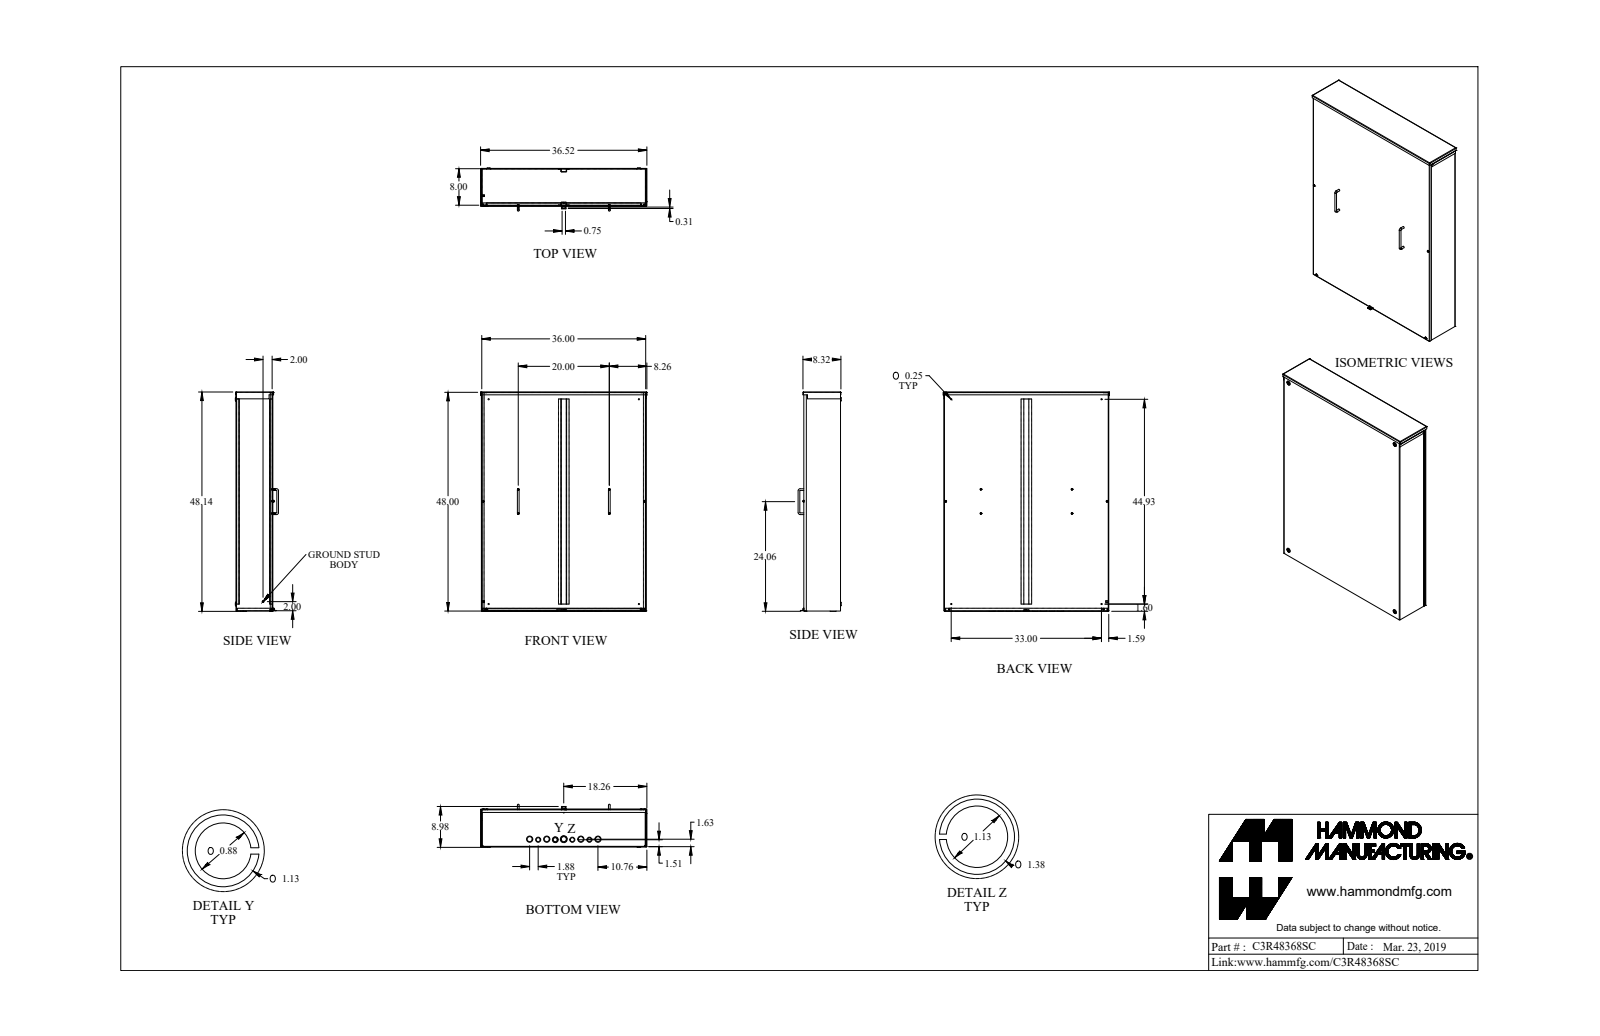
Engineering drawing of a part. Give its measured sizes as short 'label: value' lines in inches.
name: C3R48368SC_Default
written by: SolidWorks 2019 (CONFIG_CONTROL_DESIGN)
unit: in
bodies: 19 solids, 653 faces (342 planar, 193 cylindrical, 118 other)
size: 48.144 × 36.519 × 9.478
volume: 385.5 in³; area: 10 737 in²
holes: 5× ⌀0.156, 4× ⌀0.17, 4× ⌀0.203, 4× ⌀0.25, 4× ⌀0.875, 3× ⌀1.125, 2× ⌀1.125, 1× ⌀0.125, 1× ⌀0.137
bosses: 11× ⌀0.375, 8× ⌀0.19, 5× ⌀1.375, 4× ⌀1.125, 4× ⌀0.367, 1× ⌀0.125
rounds: 28× R0.036, 28× R0.108, 8× R0.109, 8× R0.125, 2× R0.156, 1× R0.029, 1× R0.086
face distances: 0.072, 8, 7.928, 8.072, 35.928, 48, 36, 35.856, 47.928, 48.072
hole spacings: 20, 7.5, 0.061, 1.879, 1.88, 3.75, 5.3, 5.627
